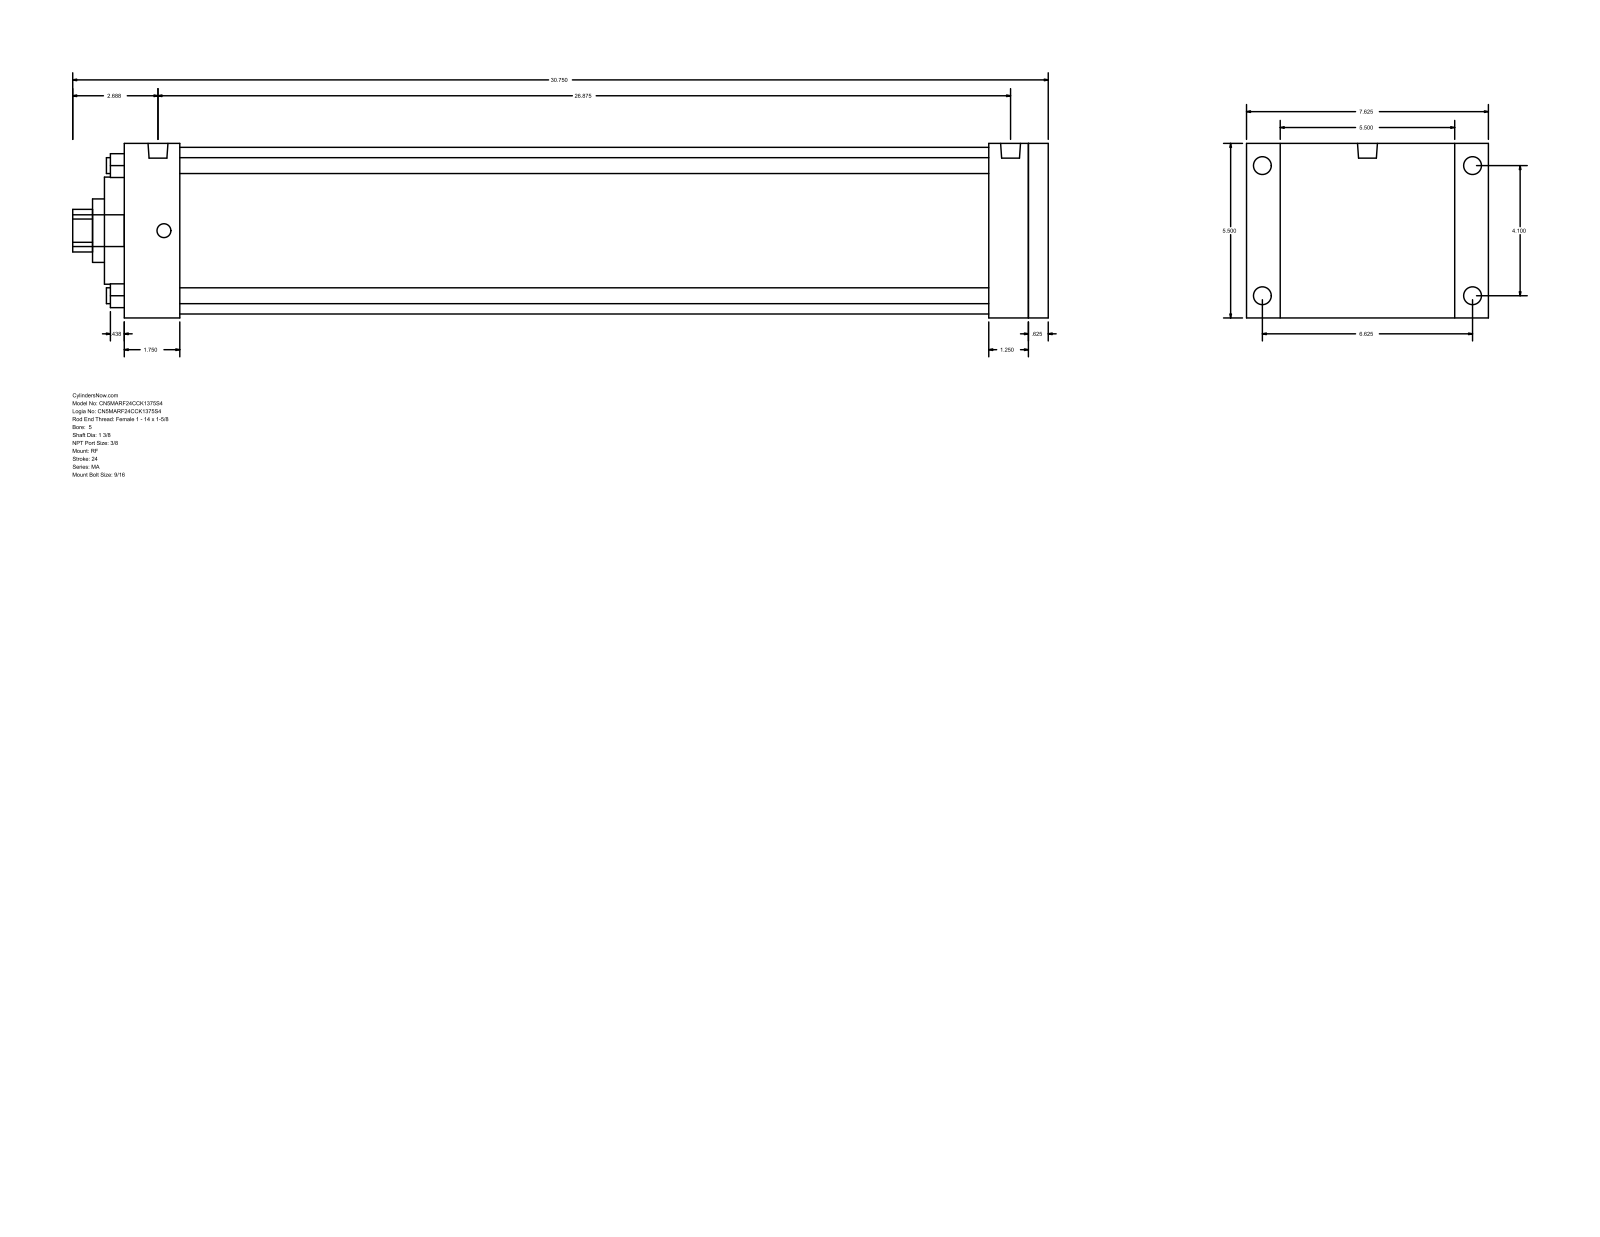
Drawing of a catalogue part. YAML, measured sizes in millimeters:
part_name: "MA_RF__0500_1.375"
step_written_by: "GSSL Pune (CONFIG_CONTROL_DESIGN)"
units: millimeters
bodies: {solids: 0, faces: 94, planar: 65, cylindrical: 29, other: 0}
overall_size: [781.05, 193.68, 139.7]
round_holes:
  - {diameter: 12.7, count: 4}
  - {diameter: 34.92, count: 1}
  - {diameter: 50.8, count: 1}
  - {diameter: 85.72, count: 1}
  - {diameter: 133.35, count: 1}
round_bosses_or_shafts:
  - {diameter: 14.29, count: 4}
  - {diameter: 11.11, count: 4}
  - {diameter: 15.93, count: 2}
  - {diameter: 25.4, count: 1}
partial_cylinders:
  - {radius: 17.06, count: 1}
face_to_face_distances: [139.7, 739.78, 15.88, 723.9, 44.45, 679.45, 695.33, 692.15, 647.7, 31.75]
hole_center_spacings: [73.64, 104.14, 147.28]
